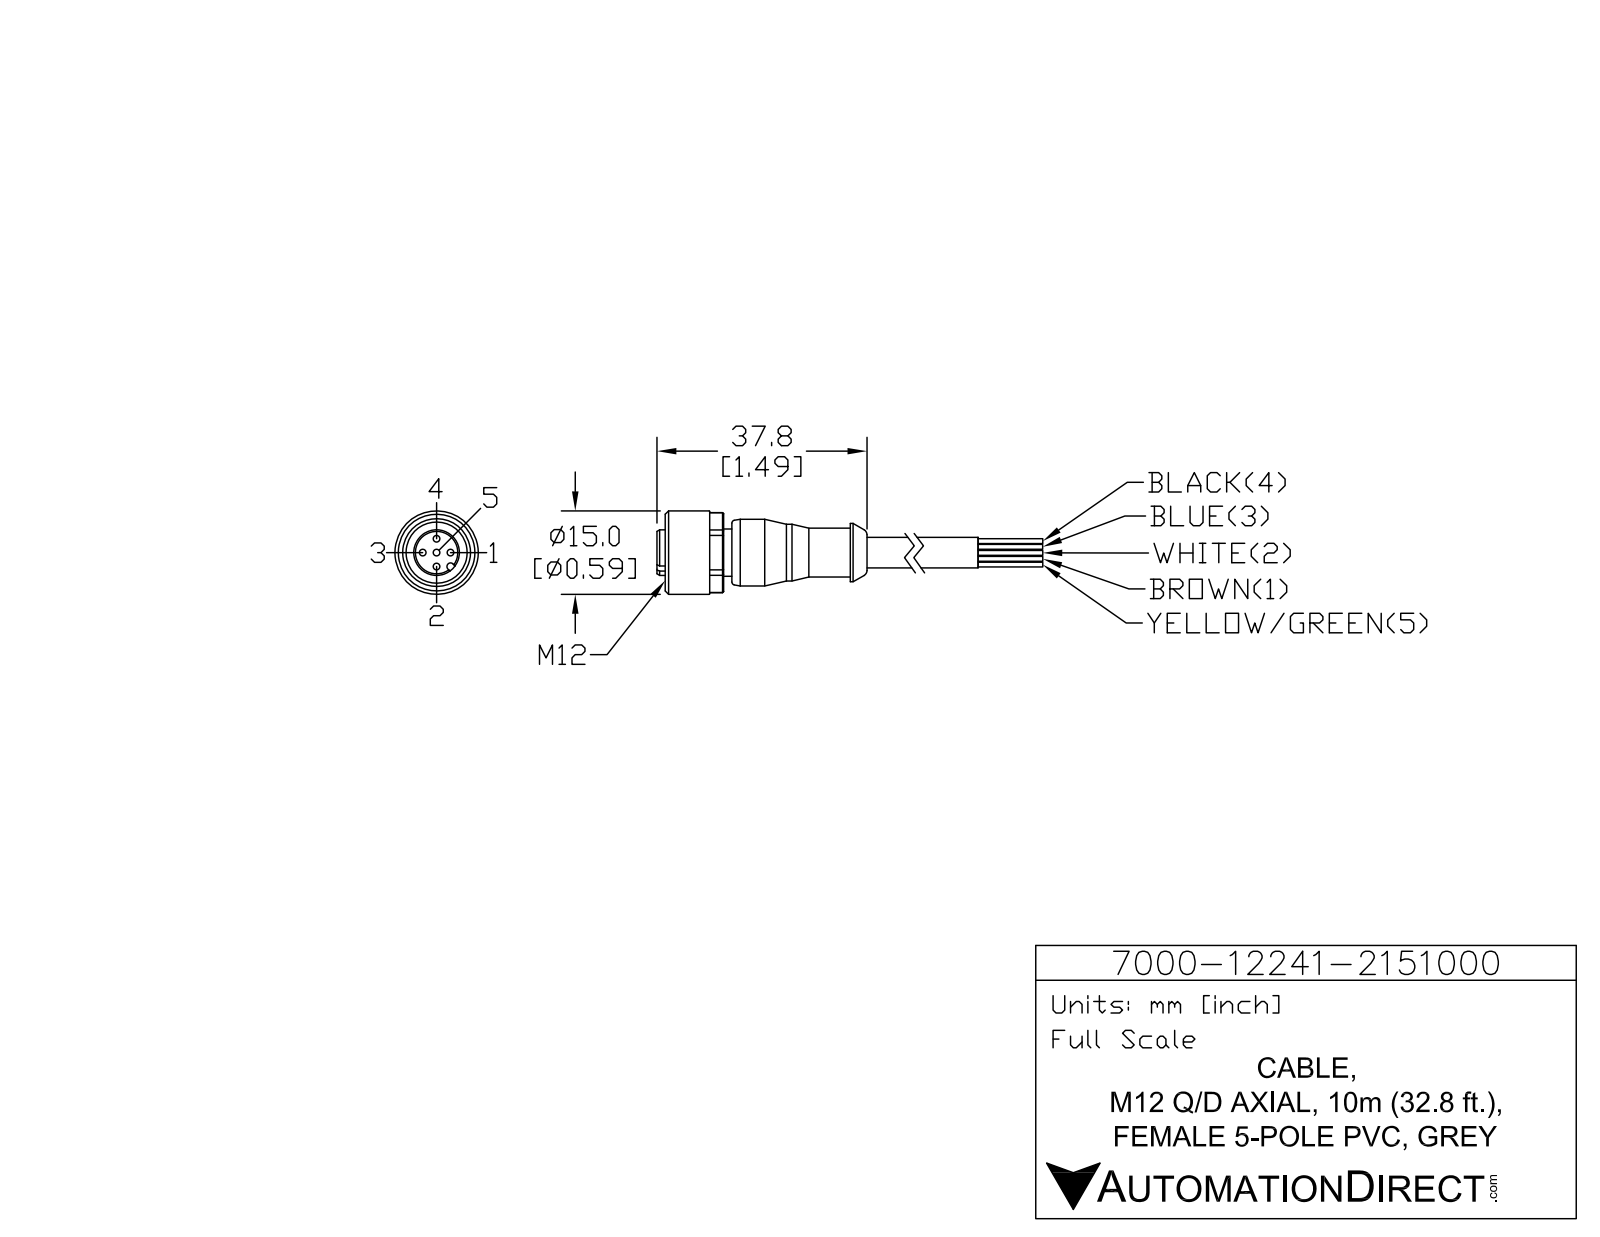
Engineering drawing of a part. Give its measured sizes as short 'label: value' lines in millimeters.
name: 7000-12241-2151000
written by: SolidWorks 2015 (AUTOMOTIVE_DESIGN)
unit: mm
bodies: 1 solid, 93 faces (29 planar, 36 cylindrical, 28 other)
size: 57.8 × 15 × 15
volume: 4 024 mm³; area: 2 667 mm²
holes: 5× ⌀1.2, 1× ⌀11
bosses: 1× ⌀15, 1× ⌀12, 1× ⌀10.5, 1× ⌀10.2, 1× ⌀8.8, 1× ⌀8.5, 1× ⌀8.2, 1× ⌀5.5
rounds: 1× R0.65, 1× R7.2
face distances: 12, 1.5, 3, 13, 9, 25.8, 7.5, 10.5, 2.5, 13.5
hole spacings: 2.5, 3.54, 5
